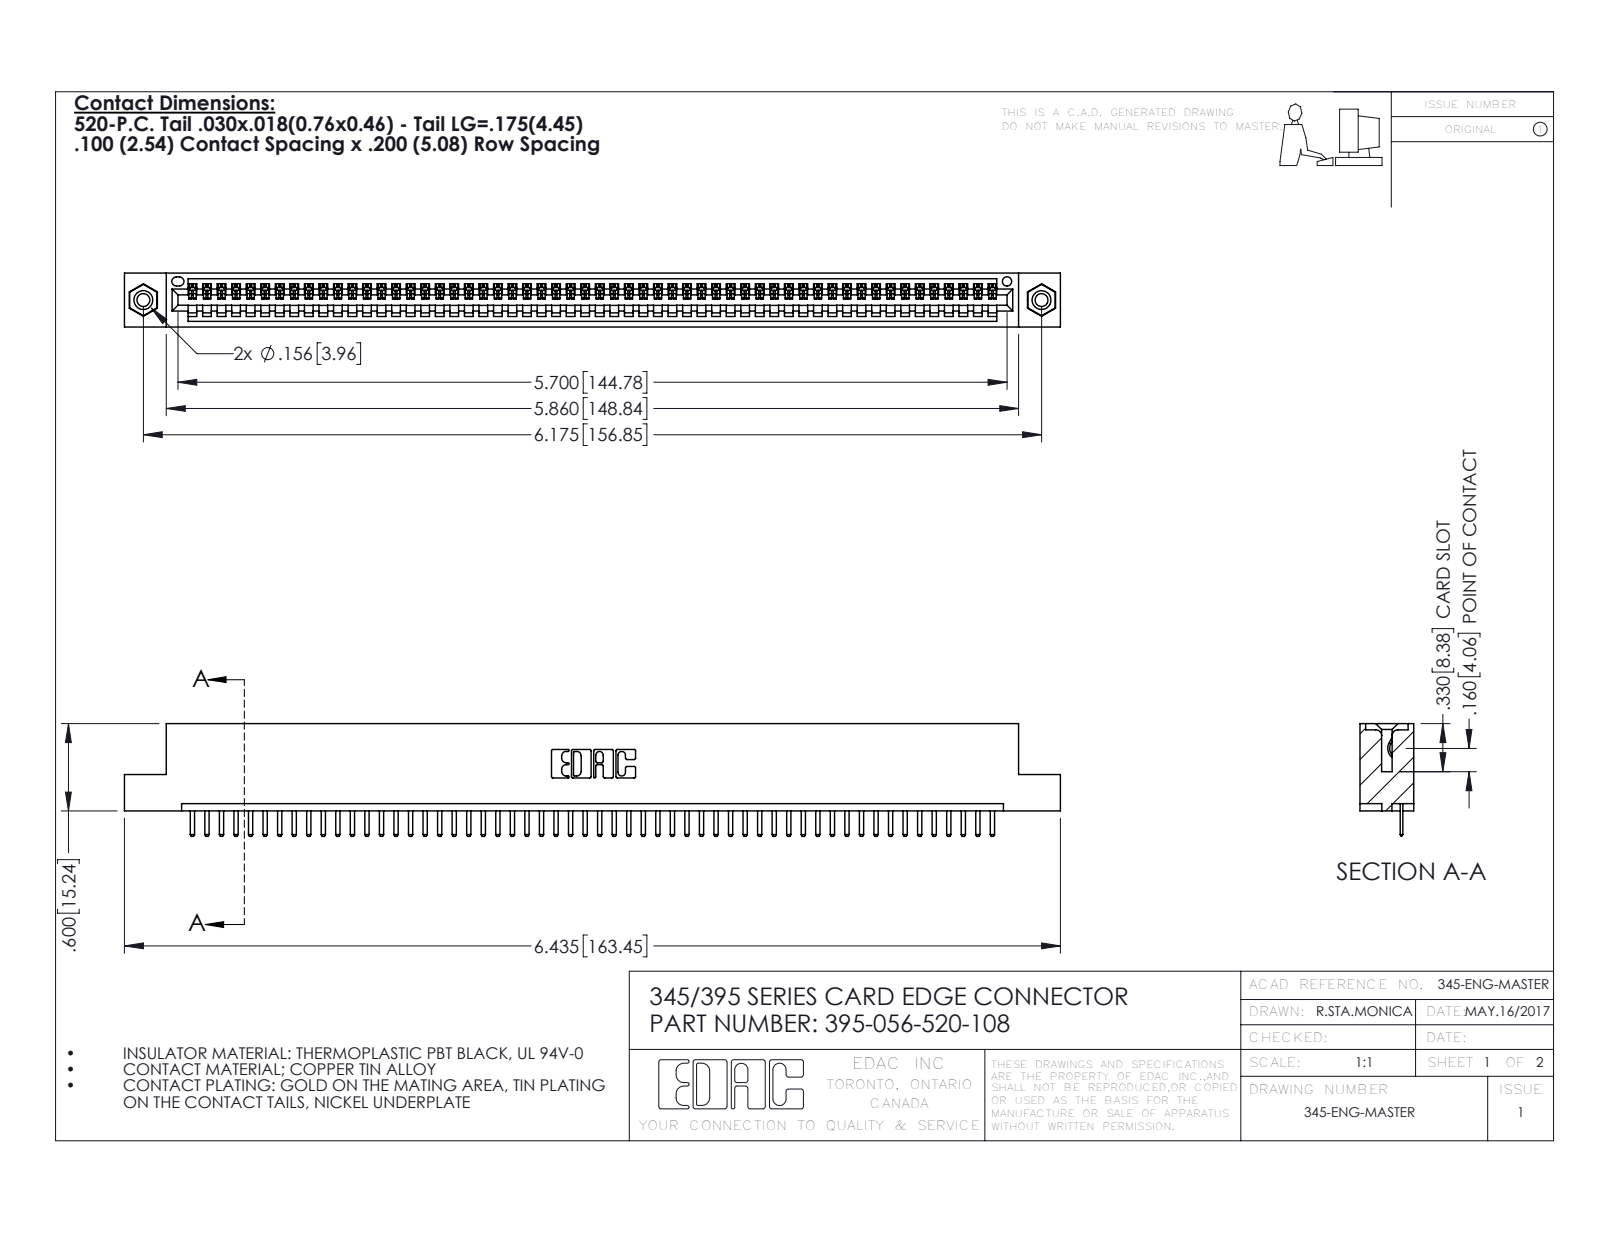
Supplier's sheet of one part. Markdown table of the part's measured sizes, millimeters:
| quantity | value |
| --- | --- |
| part name | 395-056-520-108; 345-292-001_345-293-120; 345 Part_Flush Mounting Lugs - 0.156 Dia-TI; 345-250-001_345-250-003-102 |
| STEP written by | SolidWorks 2016 (CONFIG_CONTROL_DESIGN) |
| units | millimeters |
| bodies | 59 solids, 3658 faces (2464 planar, 1178 cylindrical, 16 other) |
| overall size | 163.4 × 19.7 × 9.4 |
| volume | 15 500 mm³ |
| surface area | 20 250 mm² |
| round holes (diameter × count) | 2.3 × 2, 3.2 × 2, 4 × 2, 1.6 × 1 |
| round bosses / shafts (diameter × count) | 3.9 × 2 |
| partial cylindrical surfaces (radius × count) | 0.3 × 114, 0.2 × 112, 0.3 × 22, 0.2 × 6, 0.8 × 6, 0.7 × 3, 0.8 × 2, 1 × 2 |
| main face-to-face distances | 1.8, 7.6, 9.4, 5.1, 2.5, 6.9, 0.6, 5.7, 1.8, 3.8 |
| hole center spacings | 6.9, 150.9, 156.8 |
